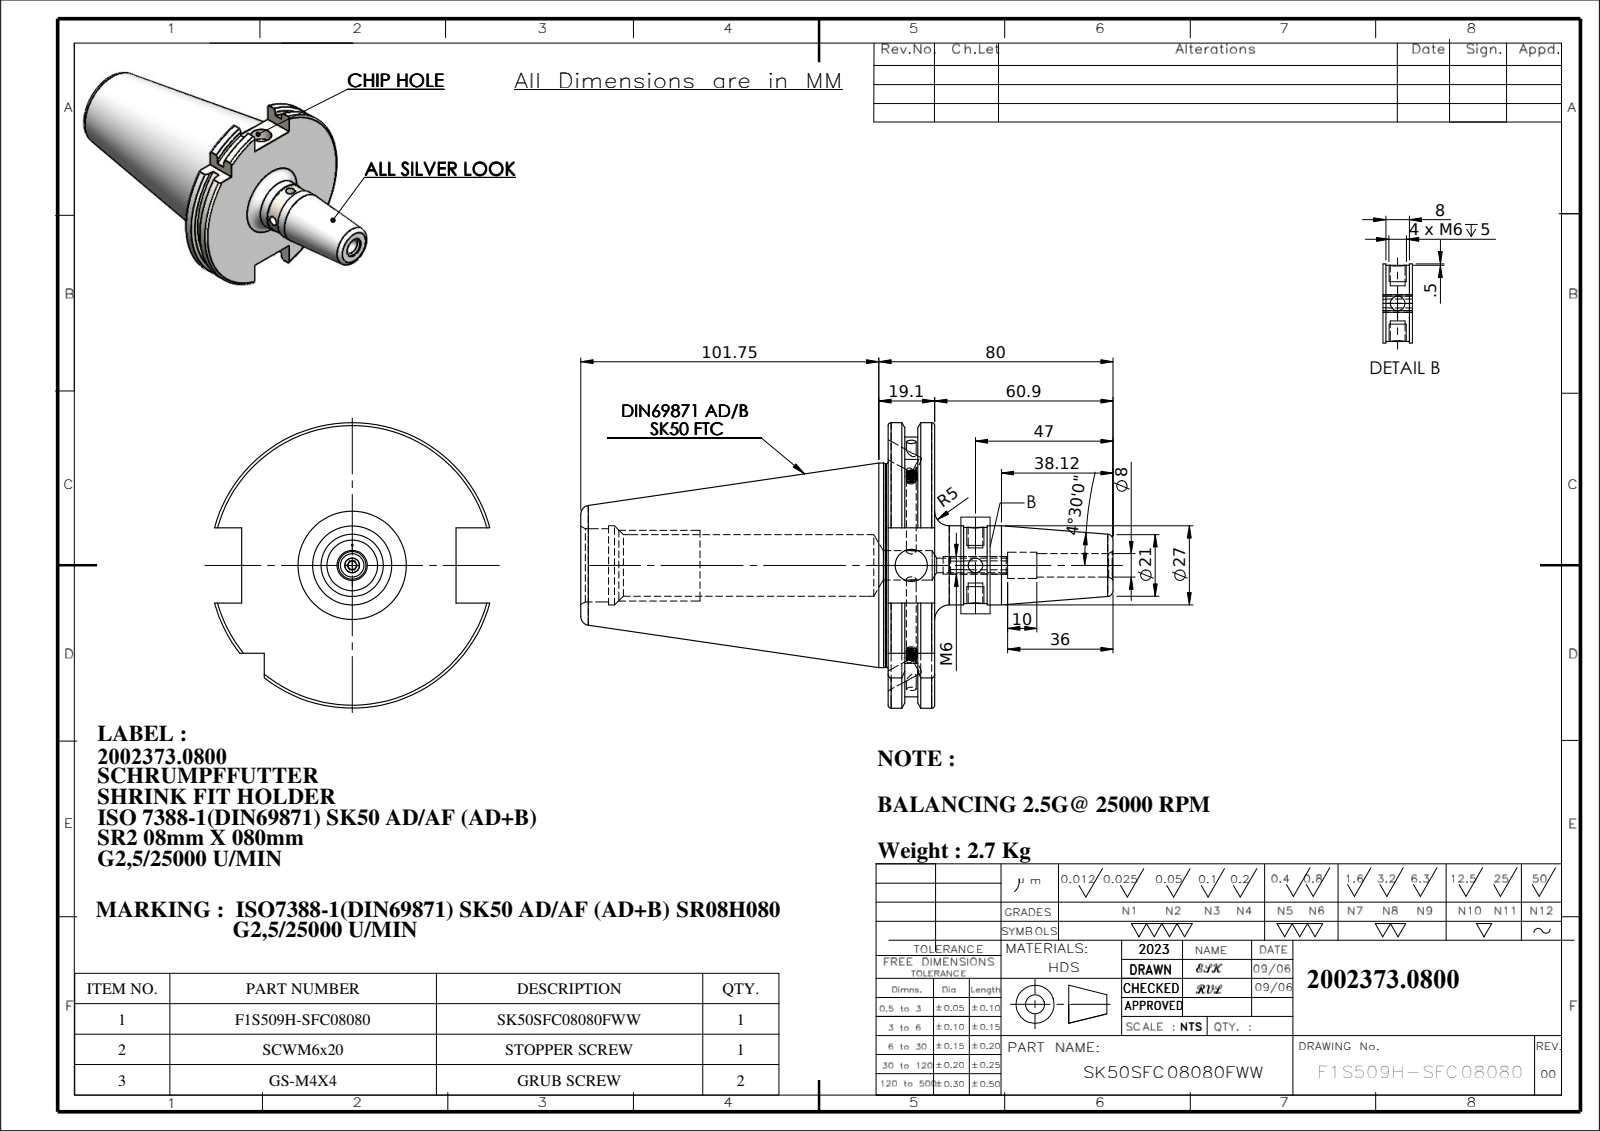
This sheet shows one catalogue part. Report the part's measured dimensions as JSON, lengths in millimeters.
{"part_name": "91506-SR208080; SK50SFC08080FWW; GS-M4X4_DIN 913 - M4 x 4-N; SCWM6", "step_written_by": "SolidWorks 2018 (CONFIG_CONTROL_DESIGN)", "units": "millimeters", "bodies": {"solids": 4, "faces": 247, "planar": 58, "cylindrical": 83, "other": 106}, "overall_size": [181.75, 97.5, 94.05], "volume_mm3": 350731, "surface_area_mm2": 51821, "round_holes": [[5, 3], [6, 2], [2.9, 1], [3.3, 1], [7.99, 1], [8.99, 1], [10, 1], [11, 1], [21, 1], [25, 1]], "round_bosses_or_shafts": [[4, 2], [69.85, 1], [69.45, 1], [27, 1], [26, 1], [6, 1]], "partial_cylinders_radius": [[44.9, 1], [48.75, 1]], "face_to_face_distances": [15.9, 5.66, 10.24, 10.15, 4.49, 5.75, 104.95, 110.61, 115.1, 120.85], "hole_center_spacings": [21.9]}
